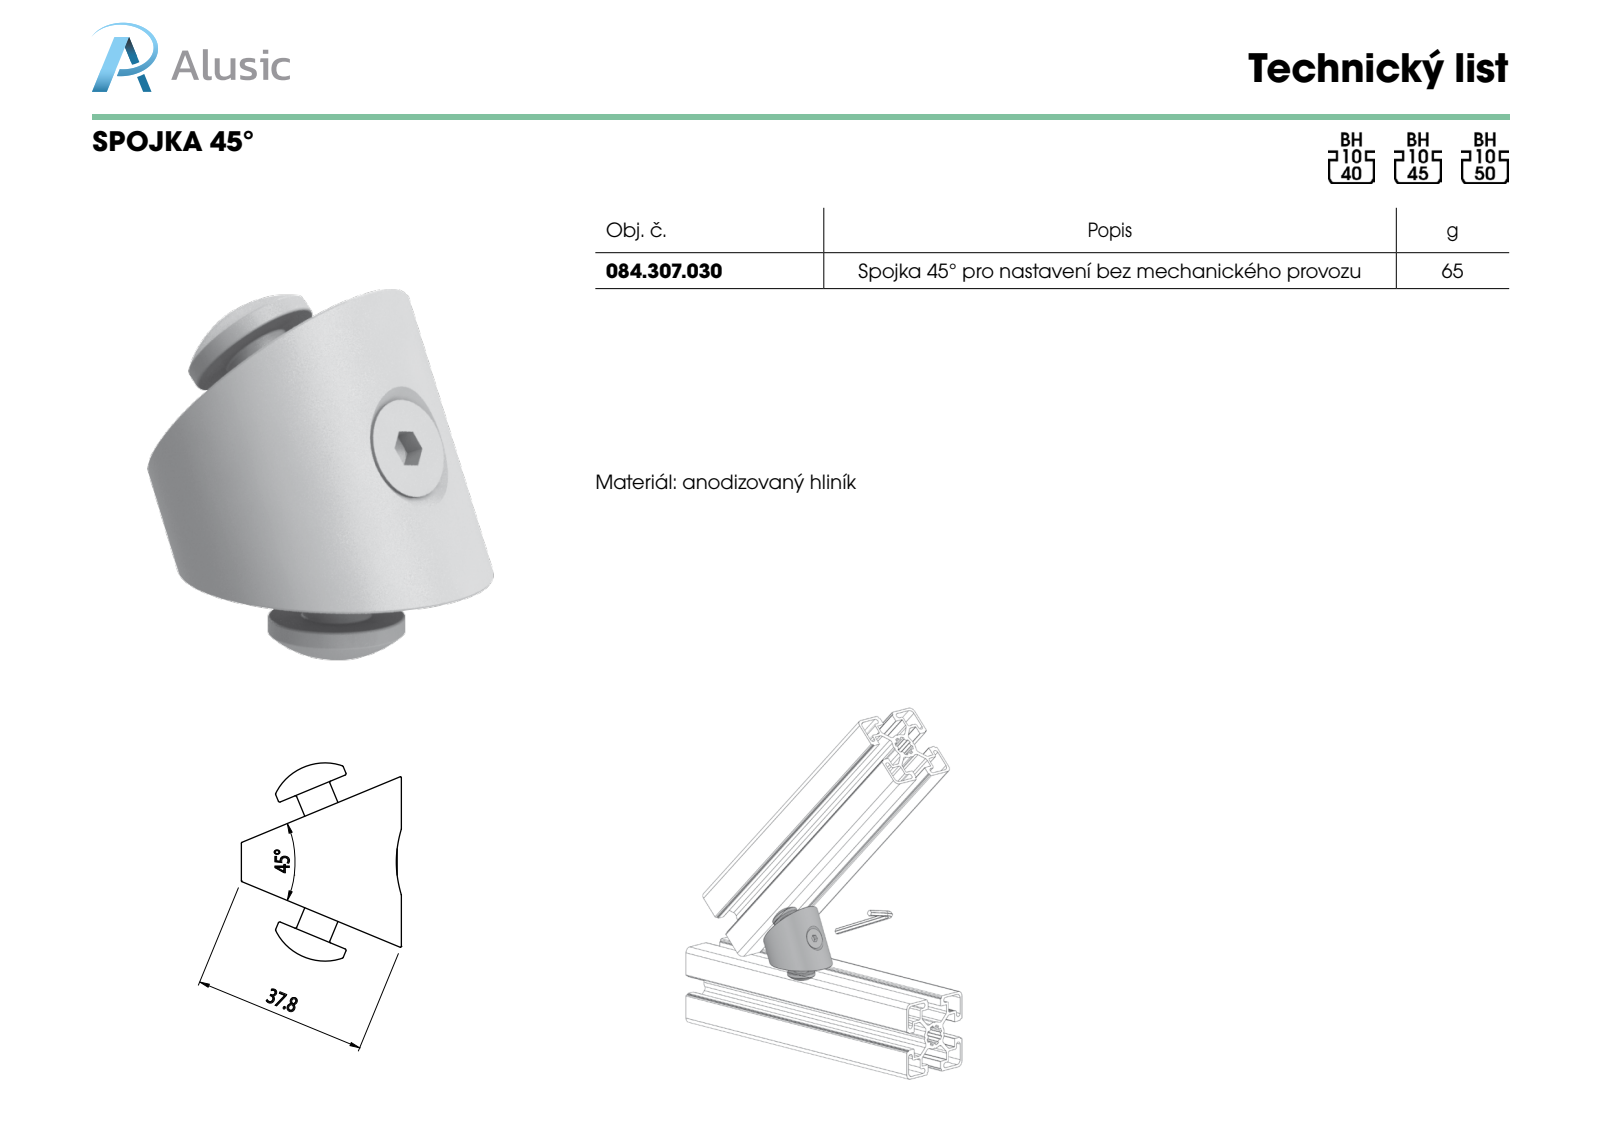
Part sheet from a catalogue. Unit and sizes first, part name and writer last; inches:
Units: inches
Overall size (bounding box): 1.705 × 1.378 × 1.378
Round holes (diameter × count): ⌀0.197 ×1, ⌀0.26 ×1, ⌀0.984 ×1
Round bosses / shafts (diameter × count): ⌀0.63 ×2, ⌀0.309 ×2, ⌀1.378 ×1, ⌀0.456 ×1, ⌀0.236 ×1
Partial cylindrical surfaces — rounded edges, fillets, slot ends (radius × count): R0.276 ×1
Main face-to-face distances: 0.195, 0.335, 0.747, 0.412, 0.237, 0.572, 0.984, 0.158, 0.886, 0.648
Volume: 0.902 in³ · Surface area: 12.86 in²
Bodies: 3 solids, 228 faces (20 planar, 60 cylindrical, 148 other)
Part name (STEP PRODUCT): 084.307.030
STEP written by: SolidWorks 2011 (CONFIG_CONTROL_DESIGN)
